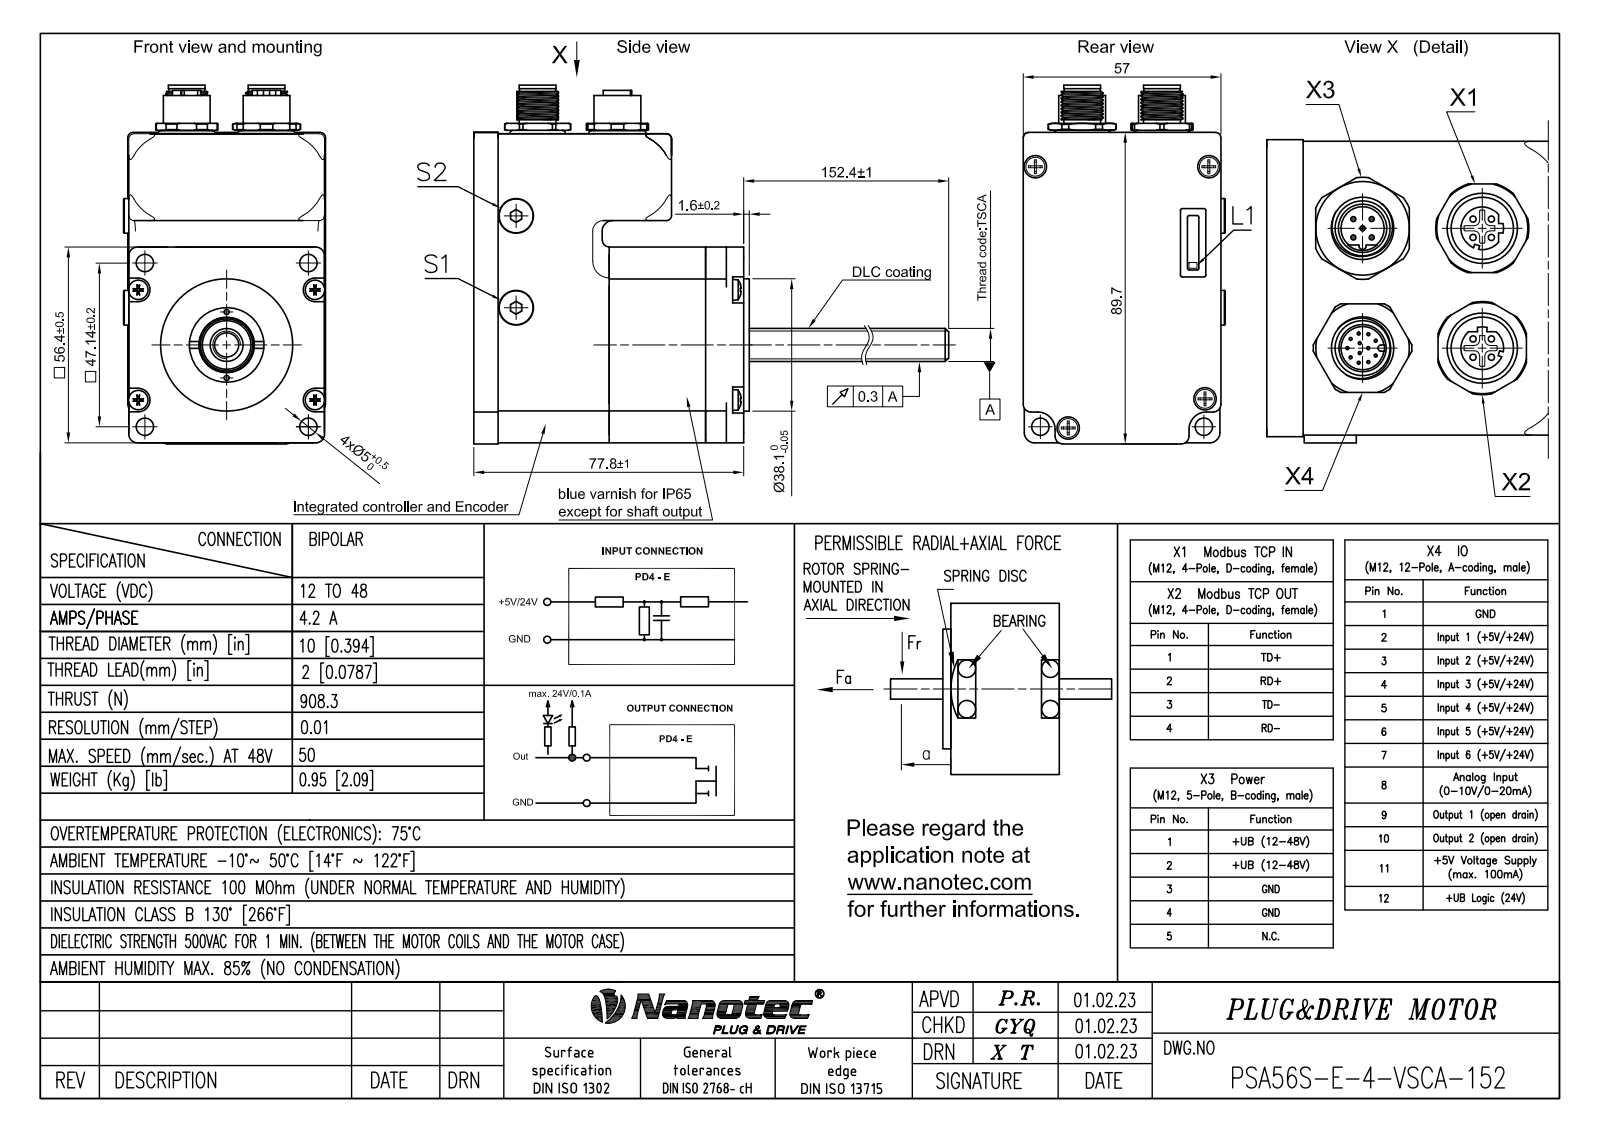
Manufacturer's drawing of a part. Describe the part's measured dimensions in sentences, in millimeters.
The part is named "零件19". Its 3-D file was written by "Autodesk Inventor 2020 (CONFIG_CONTROL_DESIGN)". It is 2 solids with 1196 faces: 502 planar, 381 cylindrical and 313 other. Overall it measures 230.2 by 103.3 by 58.2 millimeters. Its volume is 212 217 cubic millimeters and its surface area 77 329 square millimeters. Round holes: 8 of diameter 1.2, 6 of diameter 2.5, 4 of diameter 3.2, 4 of diameter 3.4, 4 of diameter 5, 4 of diameter 15.3, 3 of diameter 11, 2 of diameter 1.5, 2 of diameter 2.46, 2 of diameter 12, 1 of diameter 7, 1 of diameter 8.3. Round bosses or shafts: 17 of diameter 1, 13 of diameter 1.6, 12 of diameter 0.6, 8 of diameter 3, 4 of diameter 5.5, 4 of diameter 2.69, 4 of diameter 2.67, 3 of diameter 15.2. Partial cylindrical surfaces (rounded edges, fillets, slot ends): 20 of radius 2, 12 of radius 0.2, 12 of radius 0.5, 12 of radius 2.2, 11 of radius 0.3, 10 of radius 1.5, 8 of radius 1, 8 of radius 2.3. The main face-to-face distances are 2.5, 8, 56.4, 27, 3, 66.8, 53.9, 19, 47.8, 30. The hole center spacings are 2.5, 3.54, 21.3, 23, 24.83, 7.95, 30, 39.47.
